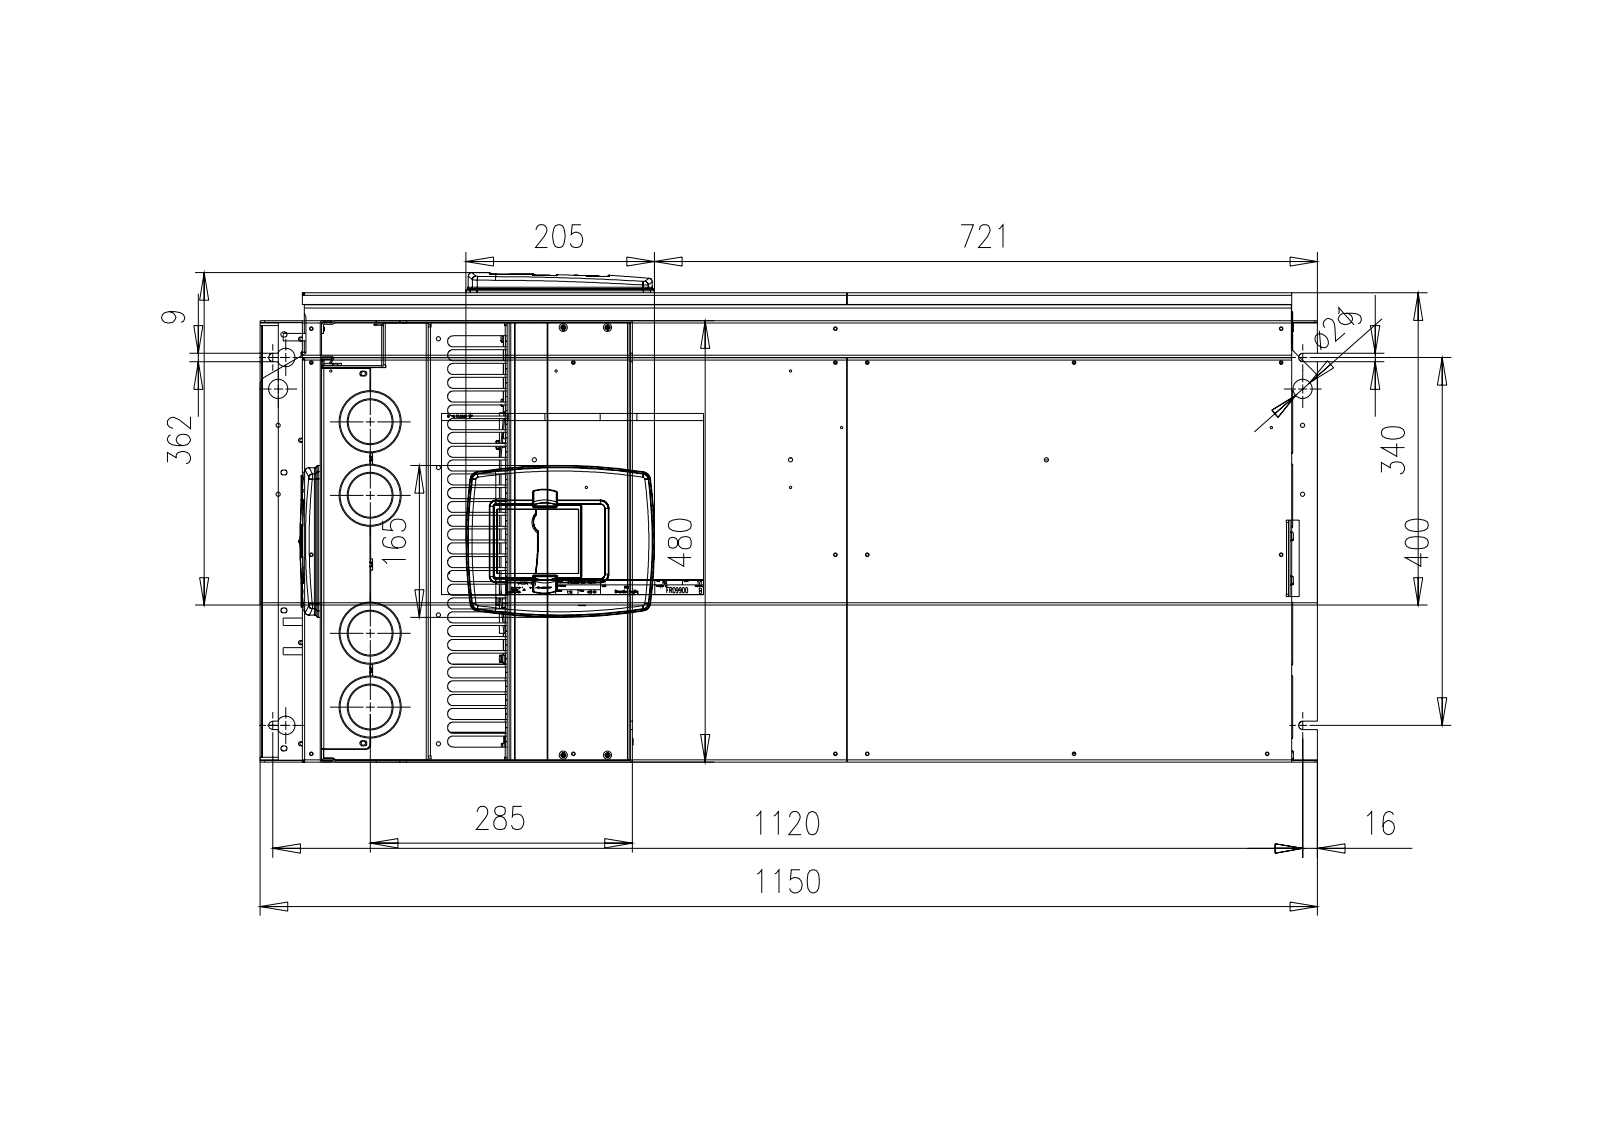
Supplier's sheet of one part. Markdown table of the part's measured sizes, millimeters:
| quantity | value |
| --- | --- |
| part name | OUT_NXP_FR9_WITHLCP |
| STEP written by | CREO PARAMETRIC BY PTC INC, 2018070 (CONFIG_CONTROL_DESIGN) |
| units | millimeters |
| bodies | 1 solid, 2413 faces (1107 planar, 1057 cylindrical, 249 other) |
| overall size | 1150 × 480 × 361.31 |
| volume | 169 600 000 mm³ |
| surface area | 6 386 000 mm² |
| round holes (diameter × count) | 4.5 × 27, 3.6 × 23, 4.6 × 23, 5.5 × 12, 0.6 × 8, 10 × 8, 3 × 7, 5.2 × 4, 6 × 4, 2 × 3, 21 × 3, 28 × 3 |
| round bosses / shafts (diameter × count) | 6 × 8, 3 × 8, 5.6 × 6, 0.6 × 6, 68 × 4, 18 × 4, 15.6 × 3, 10.4 × 3 |
| partial cylindrical surfaces (radius × count) | 4 × 85, 6 × 75, 0.37 × 44, 2.37 × 34, 2.5 × 22, 1 × 21, 2 × 17, 2.75 × 12 |
| main face-to-face distances | 2, 4.37, 2.37, 478, 1.5, 336, 2.2, 475.8, 2.5, 339.5 |
| hole center spacings | 80, 281.01, 558.26, 836.34, 54, 225, 481.33, 1114 |
